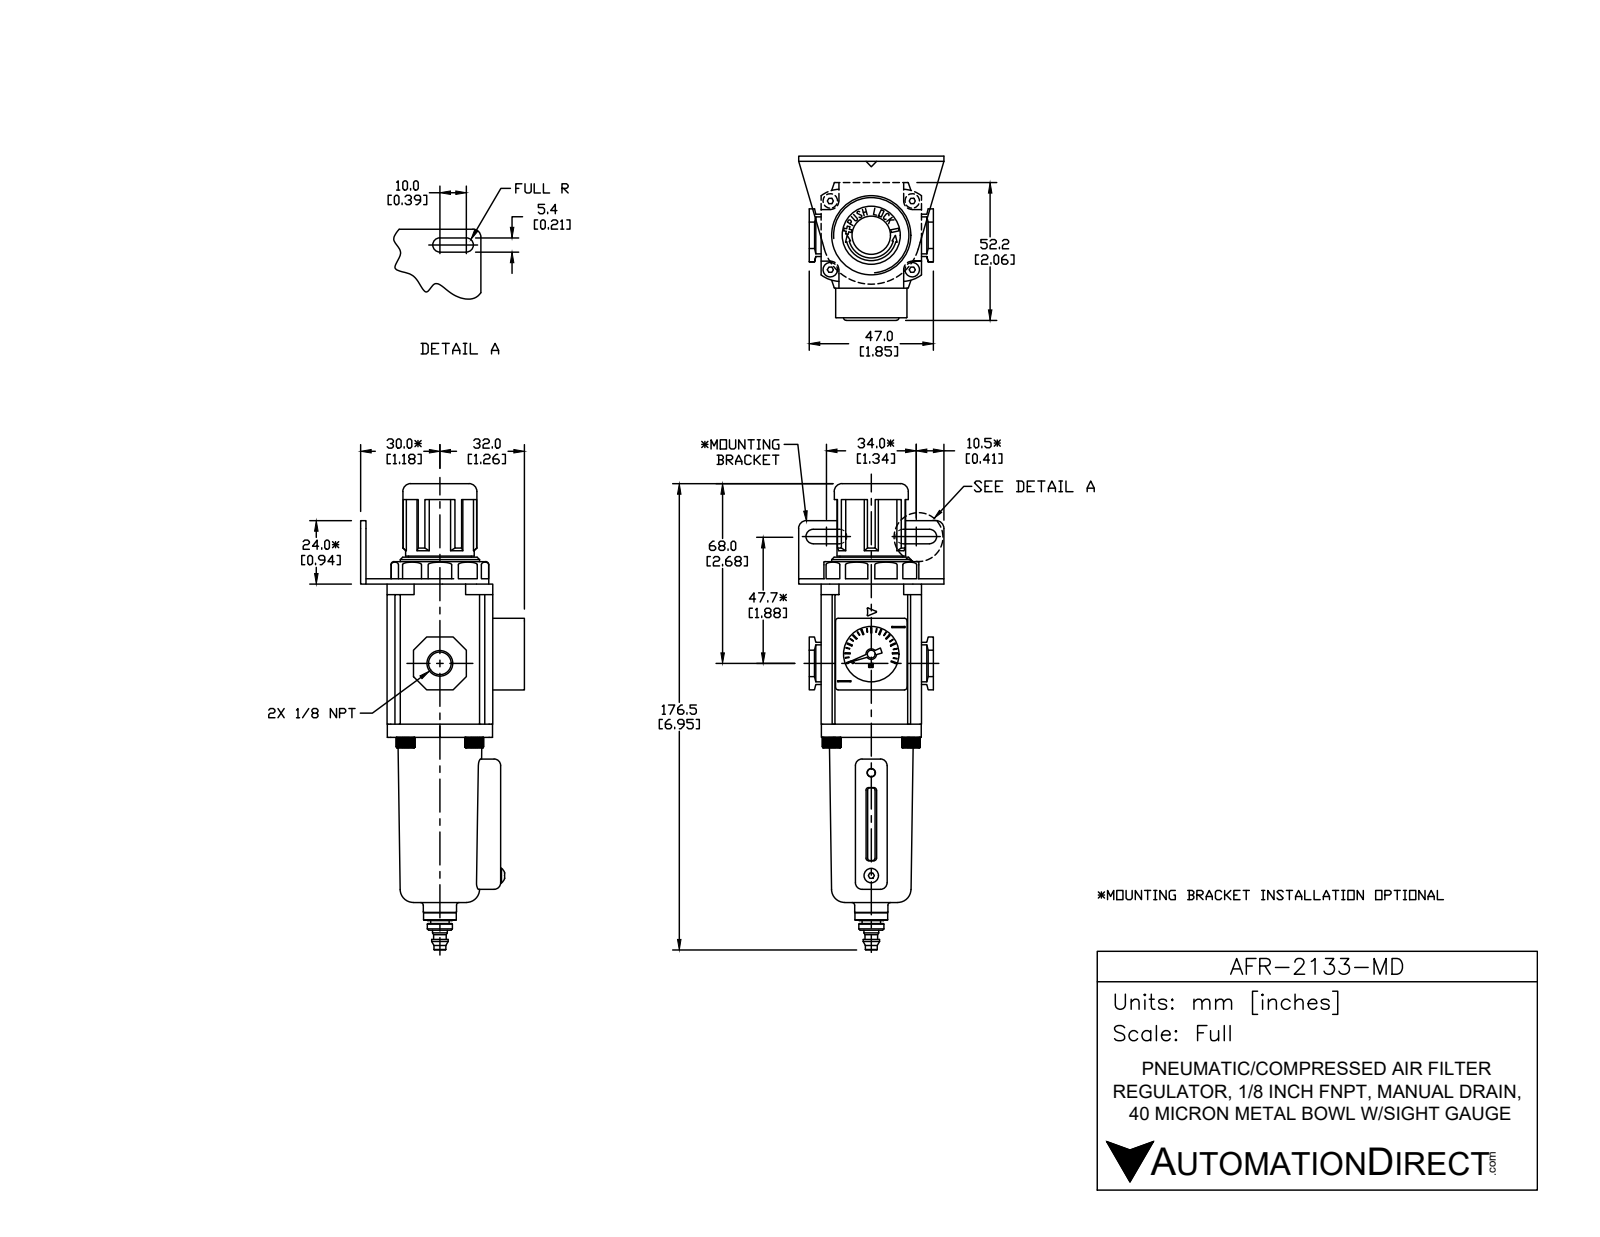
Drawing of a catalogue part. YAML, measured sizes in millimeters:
part_name: "AFR-2133-MD"
step_written_by: "SolidWorks 2015 (CONFIG_CONTROL_DESIGN)"
units: millimeters
bodies: {solids: 16, faces: 657, planar: 397, cylindrical: 190, other: 70}
overall_size: [176.5, 62, 55]
volume: 170865
surface_area: 42753
round_holes:
  - {diameter: 3, count: 7}
  - {diameter: 2, count: 1}
  - {diameter: 8.43, count: 1}
  - {diameter: 21, count: 1}
  - {diameter: 22, count: 1}
  - {diameter: 30, count: 1}
round_bosses_or_shafts:
  - {diameter: 5.5, count: 6}
  - {diameter: 7, count: 4}
  - {diameter: 2.7, count: 2}
  - {diameter: 28, count: 1}
  - {diameter: 26, count: 1}
  - {diameter: 23.8, count: 1}
  - {diameter: 14, count: 1}
  - {diameter: 12.6, count: 1}
partial_cylinders:
  - {radius: 1, count: 16}
  - {radius: 0.3, count: 12}
  - {radius: 1.2, count: 10}
  - {radius: 1.3, count: 8}
  - {radius: 2.5, count: 8}
  - {radius: 3.25, count: 6}
  - {radius: 0.5, count: 4}
  - {radius: 2.75, count: 4}
face_to_face_distances: [2, 53, 55, 40, 38, 10, 39, 1, 50, 9]
hole_center_spacings: [20.23, 14.5, 26, 31, 40.46, 28.99]
